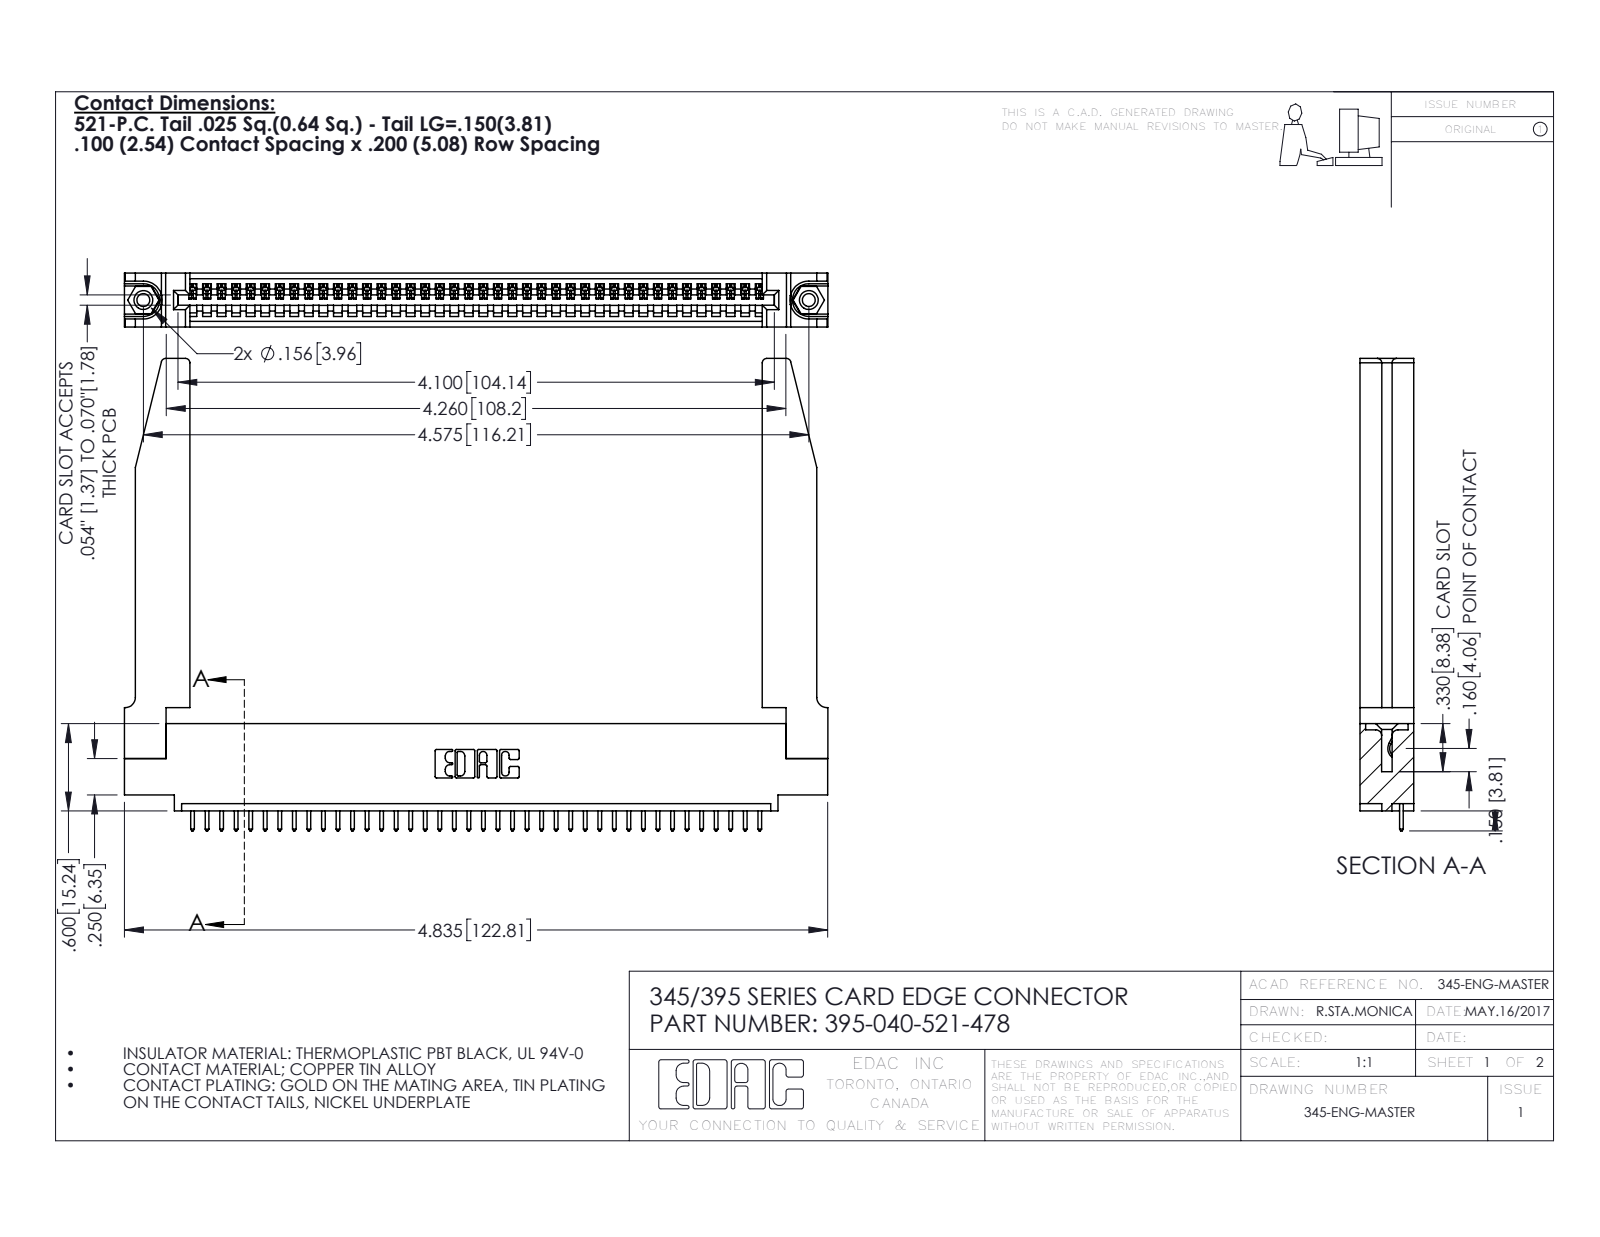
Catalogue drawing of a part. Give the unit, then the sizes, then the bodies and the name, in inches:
Units: inches
Overall size (bounding box): 4.836 × 3.247 × 0.37
Round holes (diameter × count): ⌀0.089 ×2, ⌀0.125 ×2, ⌀0.156 ×2, ⌀0.064 ×1
Round bosses / shafts (diameter × count): ⌀0.155 ×2
Partial cylindrical surfaces — rounded edges, fillets, slot ends (radius × count): R0.006 ×80, R0.01 ×80, R0.01 ×22, R0.03 ×8, R0.007 ×6, R0.031 ×6, R0.026 ×3, R0.031 ×2
Main face-to-face distances: 0.37, 0.072, 0.298, 0.2, 0.098, 0.272, 0.025, 0.225, 0.148, 0.15
Hole centre spacings: 0.27, 4.339, 4.575
Volume: 1.174 in³ · Surface area: 33.62 in²
Bodies: 45 solids, 2684 faces (1826 planar, 806 cylindrical, 52 other)
Part name (STEP PRODUCT): 345-292-001_345-293-121; 345-220-078_345-220-078; 345-250-001_345-250-001-102; 345 Part_0.110 Offset - 0.156 Dia-TH (+1 more)
STEP written by: SolidWorks 2016 (CONFIG_CONTROL_DESIGN)
